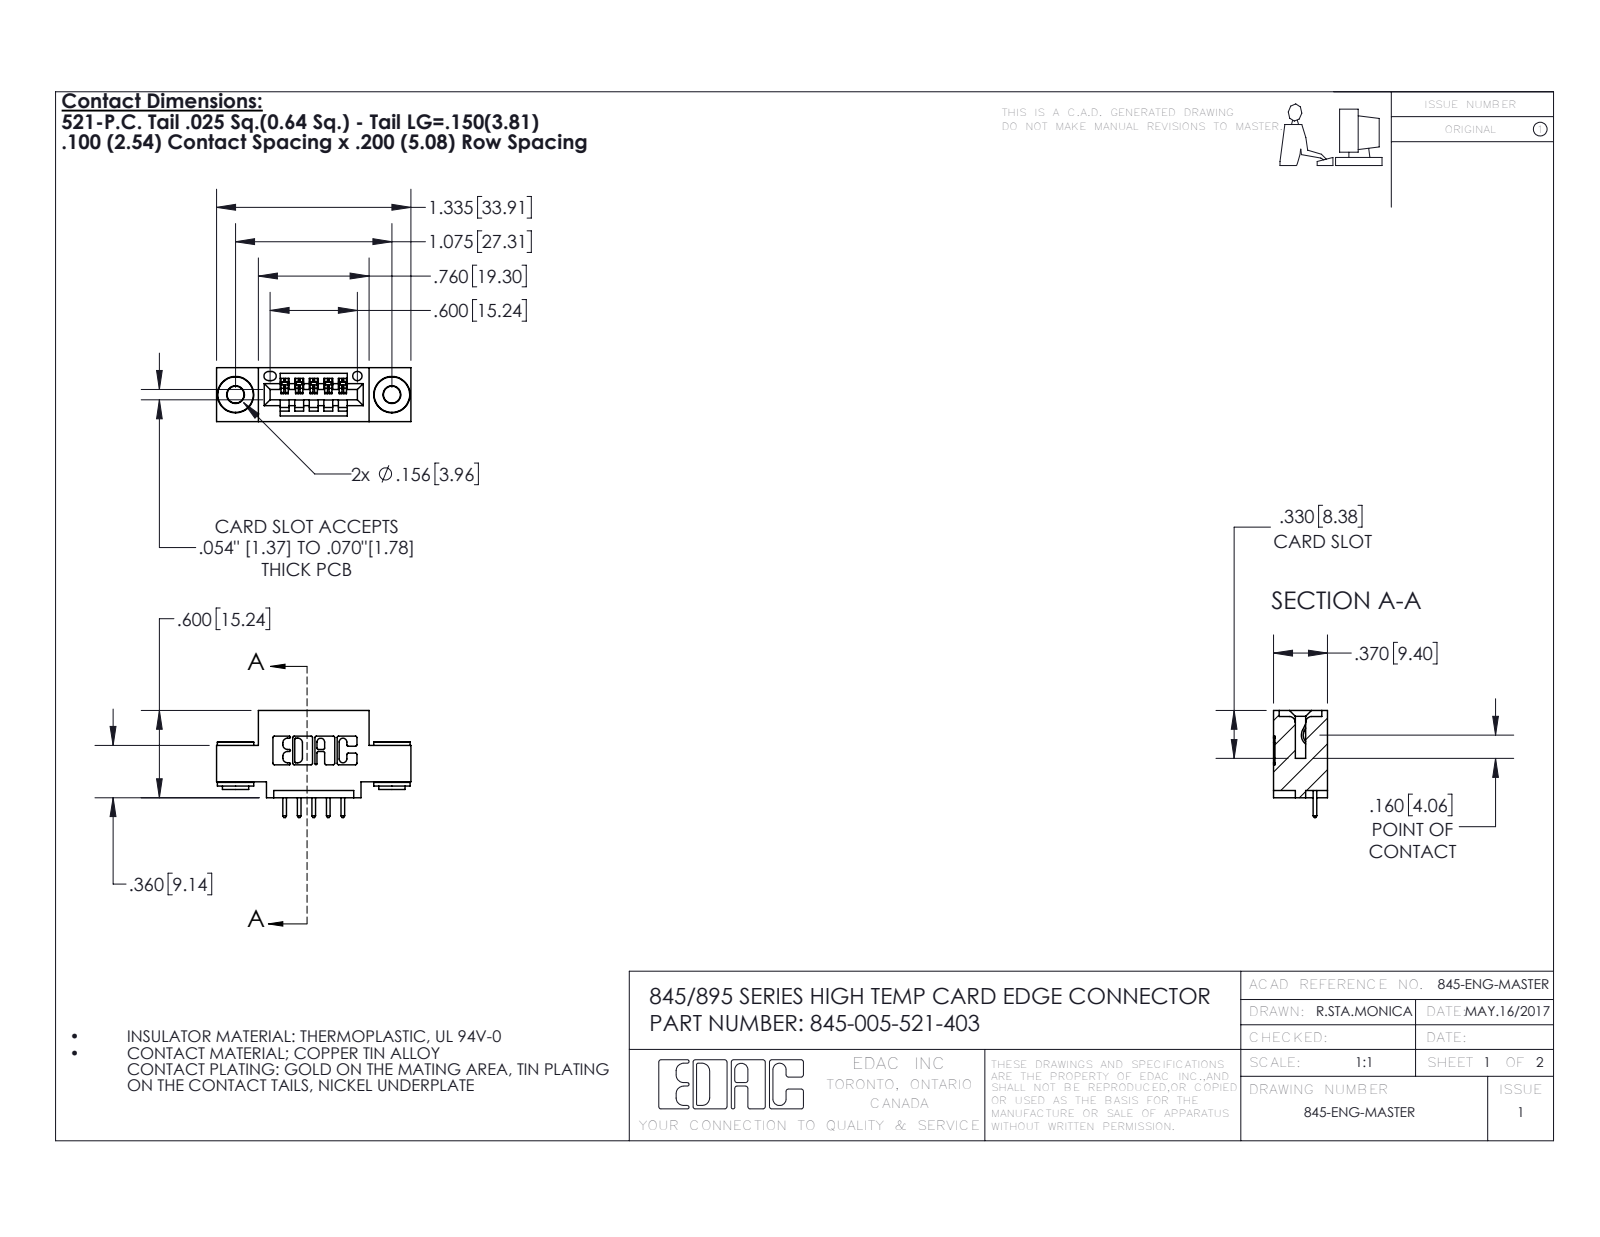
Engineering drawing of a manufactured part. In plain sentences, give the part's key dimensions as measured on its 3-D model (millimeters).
The part is named "345-292-001_345-293-121; 345-005-521-403; 345 Part_0.110 Offset - 0.156 Dia-TH; 345-250-002_345-250-002-102". Its 3-D file was written by "SolidWorks 2016 (CONFIG_CONTROL_DESIGN)". It is 8 solids with 458 faces: 294 planar, 156 cylindrical and 8 other. Overall it measures 33.9 by 18.7 by 9.4 millimeters. Its volume is 2 850 cubic millimeters and its surface area 3 525 square millimeters. Round holes: 2 of diameter 2.9, 2 of diameter 4, 1 of diameter 1.6. Round bosses or shafts: 2 of diameter 6.4, 2 of diameter 4.6, 2 of diameter 3.5. Partial cylindrical surfaces (rounded edges, fillets, slot ends): 22 of radius 0.3, 10 of radius 0.2, 10 of radius 0.3, 6 of radius 0.2, 6 of radius 0.8, 3 of radius 0.7, 2 of radius 0.8, 2 of radius 1. The main face-to-face distances are 5.1, 9.4, 1.8, 7.6, 0.6, 2.5, 6.4, 2.5, 6.9, 1.5. The hole center spacings are 6.9, 21.5, 27.3.
